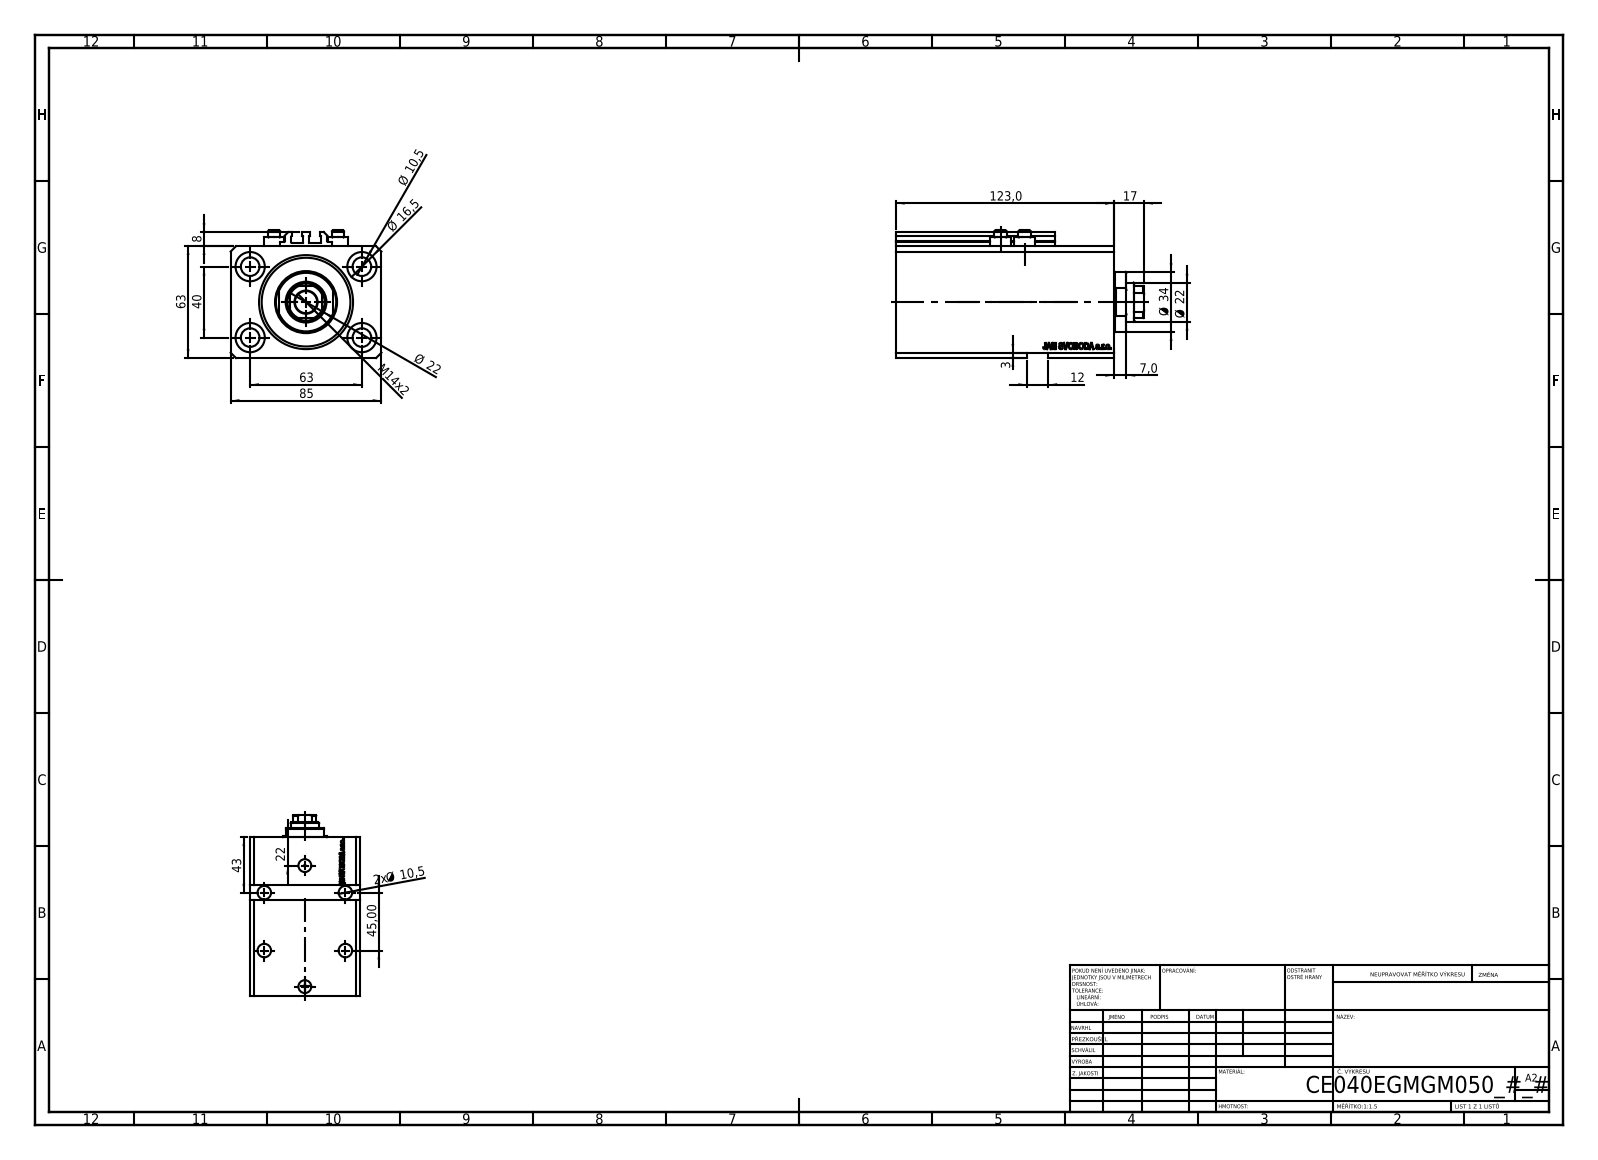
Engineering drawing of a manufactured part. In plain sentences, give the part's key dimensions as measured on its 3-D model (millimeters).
The part is named "V250CE_C_VCP; V250CE_E_Body; V250CE_VC_E; ALLEN BOLT V250CE". Its 3-D file was written by "SolidWorks 2019 (CONFIG_CONTROL_DESIGN)". It is 8 solids with 1107 faces: 535 planar, 146 cylindrical and 426 other. Overall it measures 140 by 85 by 72 millimeters. Its volume is 556 639 cubic millimeters and its surface area 119 327 square millimeters. Round holes: 8 of diameter 10.5, 4 of diameter 1.25, 4 of diameter 4, 4 of diameter 16.5, 2 of diameter 10, 2 of diameter 13.16, 2 of diameter 20, 1 of diameter 12.5, 1 of diameter 22, 1 of diameter 40, 1 of diameter 53. Round bosses or shafts: 4 of diameter 11.6, 4 of diameter 7, 1 of diameter 34. Partial cylindrical surfaces (rounded edges, fillets, slot ends): 10 of radius 0.2, 1 of radius 10.5. The main face-to-face distances are 63, 85, 123, 17, 106, 11.4, 94.6, 111.6, 3, 56. The hole center spacings are 37.31, 63, 13.6, 15.4, 24.96, 27.54, 33.62, 36.
